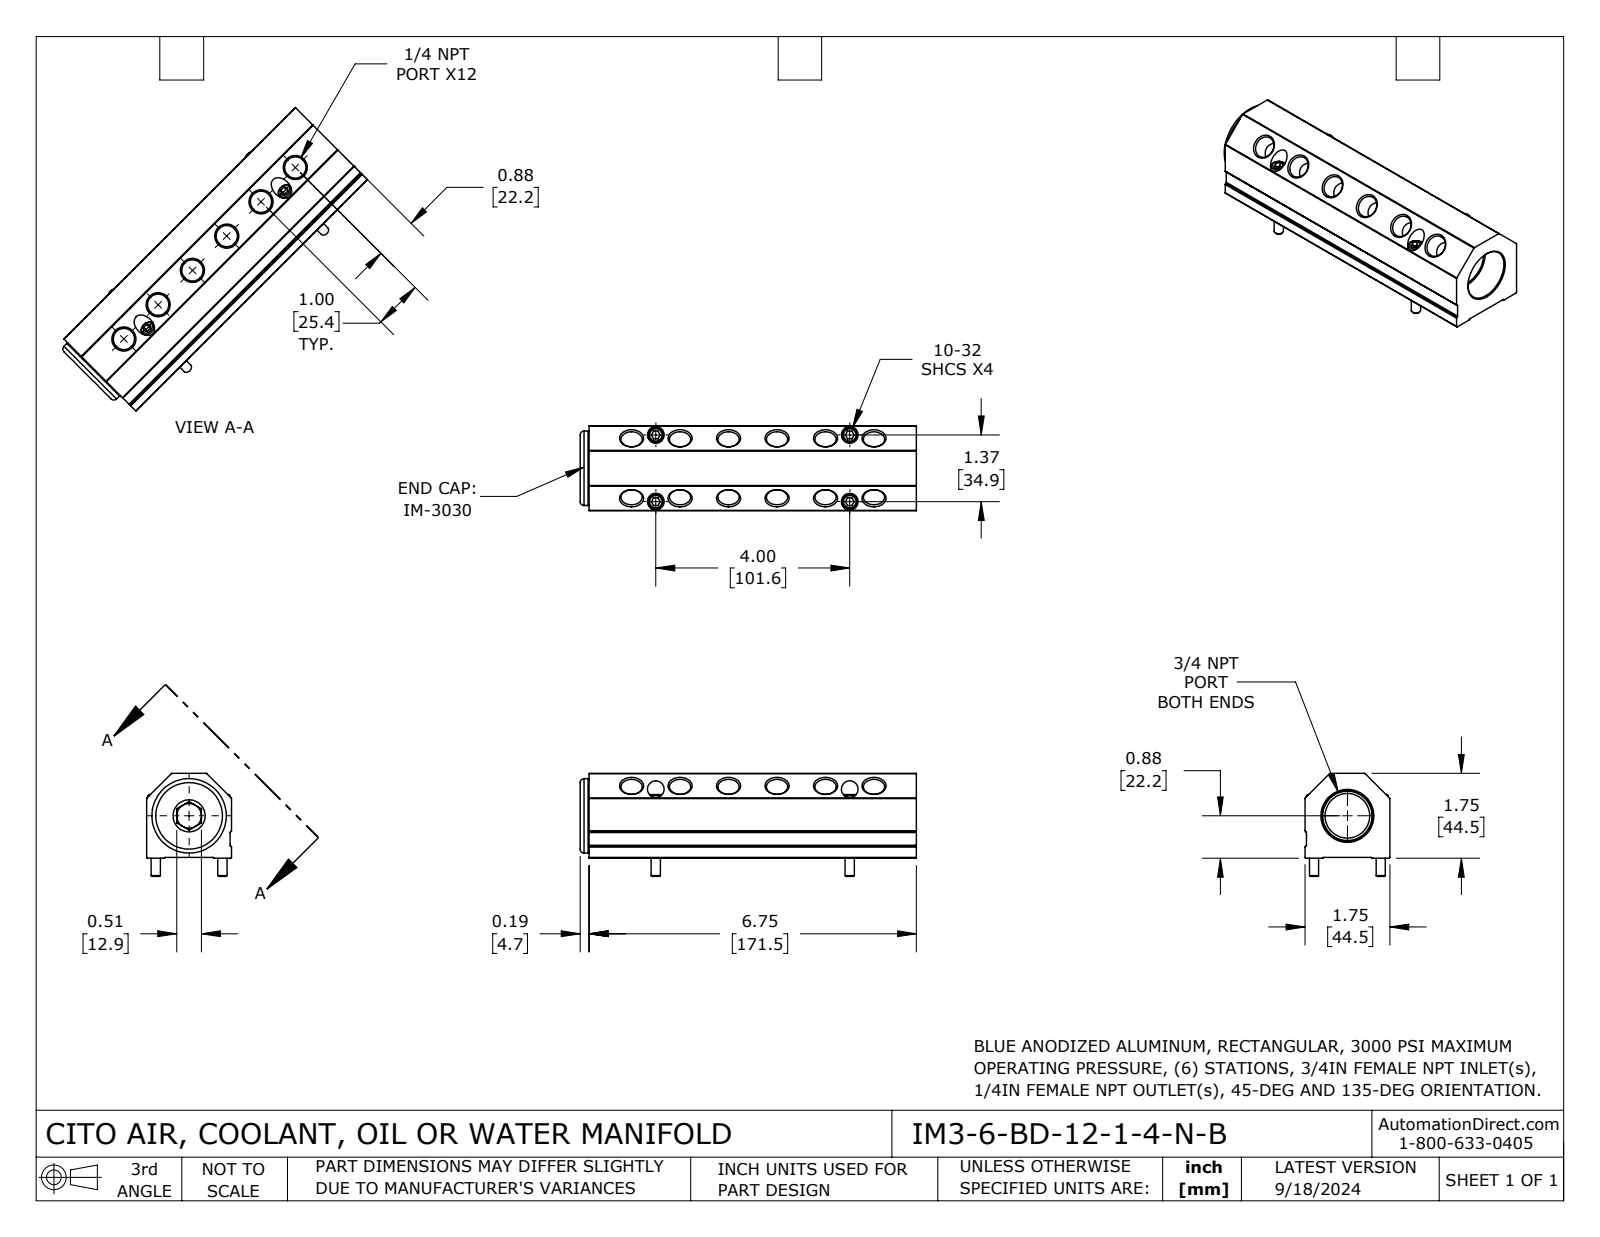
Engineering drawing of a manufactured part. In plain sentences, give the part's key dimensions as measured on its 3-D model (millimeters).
The part is named "IM3-6-BD-12-1-4-N-B". Its 3-D file was written by "SolidWorks 2023 (CONFIG_CONTROL_DESIGN)". It is 6 solids with 232 faces: 82 planar, 82 cylindrical and 68 other. Overall it measures 176.1 by 54 by 44.5 millimeters. Its volume is 224 200 cubic millimeters and its surface area 55 700 square millimeters. Round holes: 12 of diameter 11.1, 4 of diameter 5.2, 4 of diameter 8.7, 1 of diameter 13, 1 of diameter 23.4, 1 of diameter 35.4. Round bosses or shafts: 4 of diameter 7.9, 4 of diameter 4.8, 1 of diameter 39, 1 of diameter 30, 1 of diameter 23.8. Partial cylindrical surfaces (rounded edges, fillets, slot ends): 14 of radius 0.5. The main face-to-face distances are 44.5, 43.9, 0.5, 44.5, 171.5, 0.8, 43.7, 4.7, 176.1, 13.5. The hole center spacings are 25.4, 50.8, 76.2, 101.6, 34.9, 101.6, 107.4, 127.
